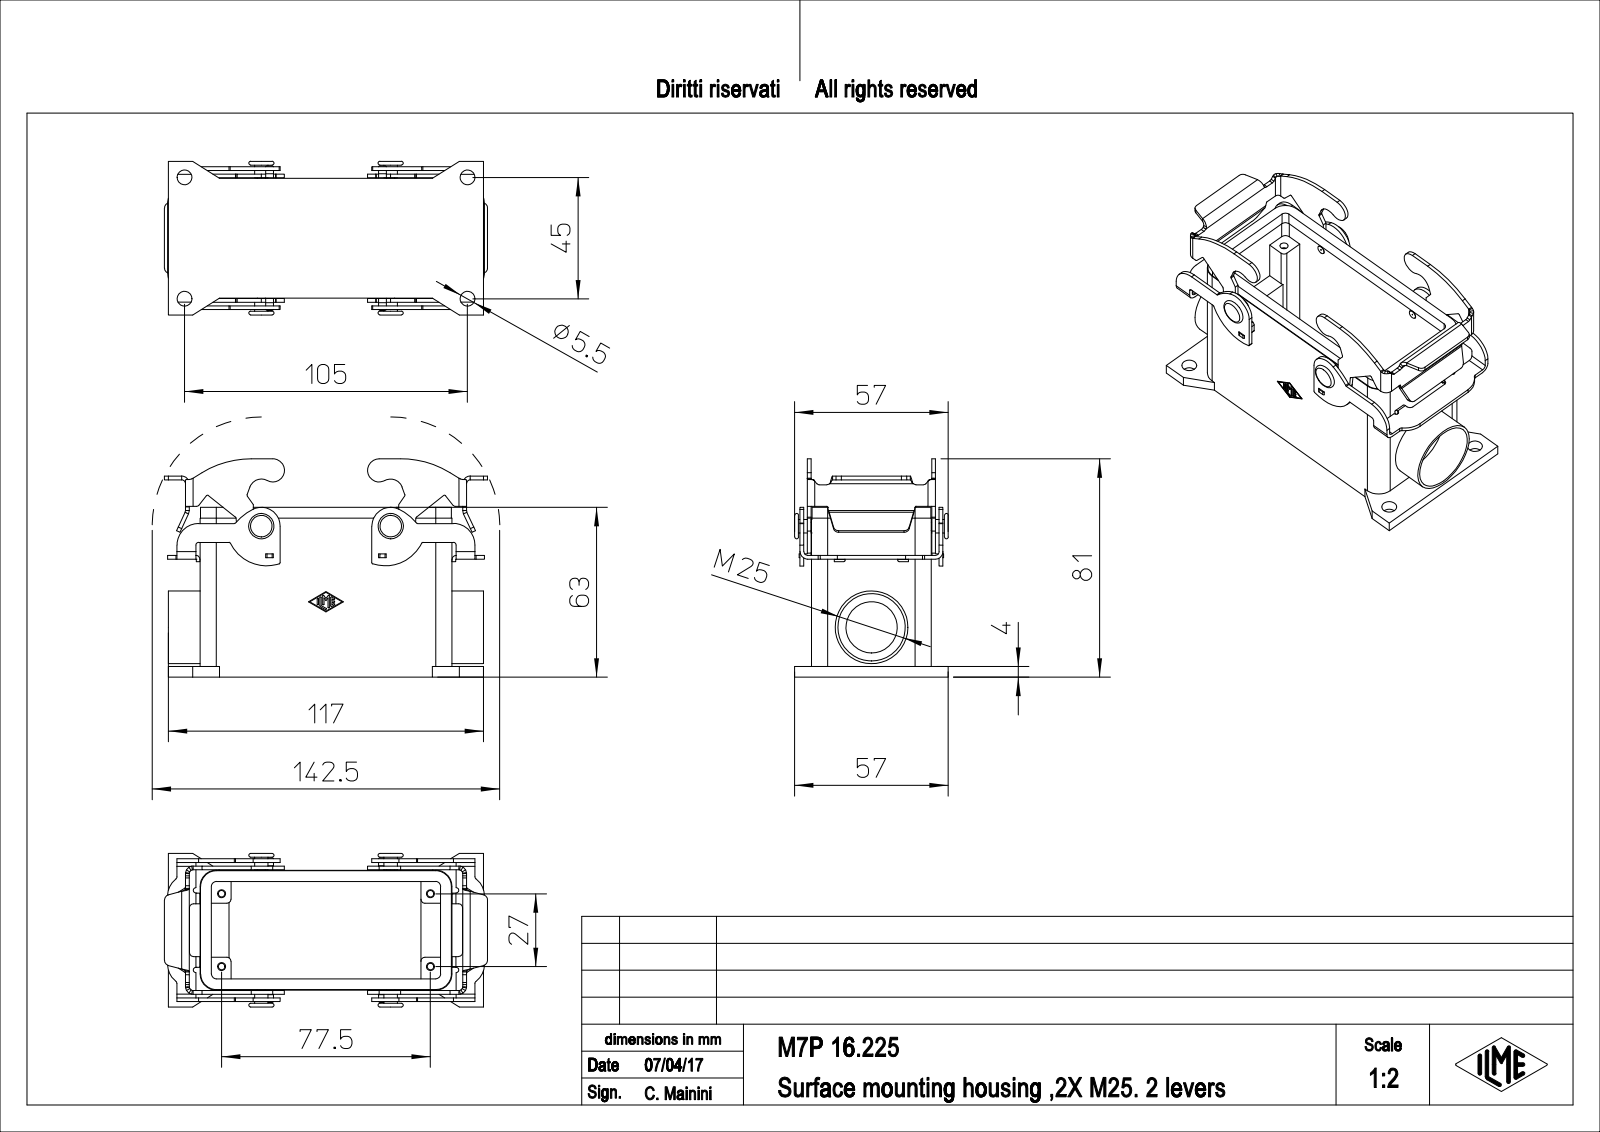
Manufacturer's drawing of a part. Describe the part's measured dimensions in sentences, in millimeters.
The part is named "M7P_16.225.stp". Its 3-D file was written by "PTC Creo Elements/Direct Modeling 19.0E 27-Jun-2016 (C) Parametric Technology GmbH (AUTOMOTIVE_DESIGN)". It is 1 solid with 608 faces: 292 planar, 270 cylindrical and 46 other. Overall it measures 119.97 by 81 by 57 millimeters. Its volume is 107 074 cubic millimeters and its surface area 63 123 square millimeters. Round holes: 4 of diameter 2.46, 4 of diameter 3, 4 of diameter 5.5, 2 of diameter 3.5, 1 of diameter 19, 1 of diameter 25. Round bosses or shafts: 2 of diameter 5, 2 of diameter 3.2, 2 of diameter 3, 1 of diameter 27. Partial cylindrical surfaces (rounded edges, fillets, slot ends): 22 of radius 0.5, 18 of radius 1, 16 of radius 0.25, 14 of radius 1.5, 12 of radius 2, 10 of radius 1.4, 10 of radius 2.8, 6 of radius 8. The main face-to-face distances are 4, 40.5, 1.4, 44.5, 36.5, 2.7, 48.9, 1.55, 5.55, 8.25. The hole center spacings are 16.43, 38.54, 91.69, 98.09, 27, 45, 77.5, 82.07.
